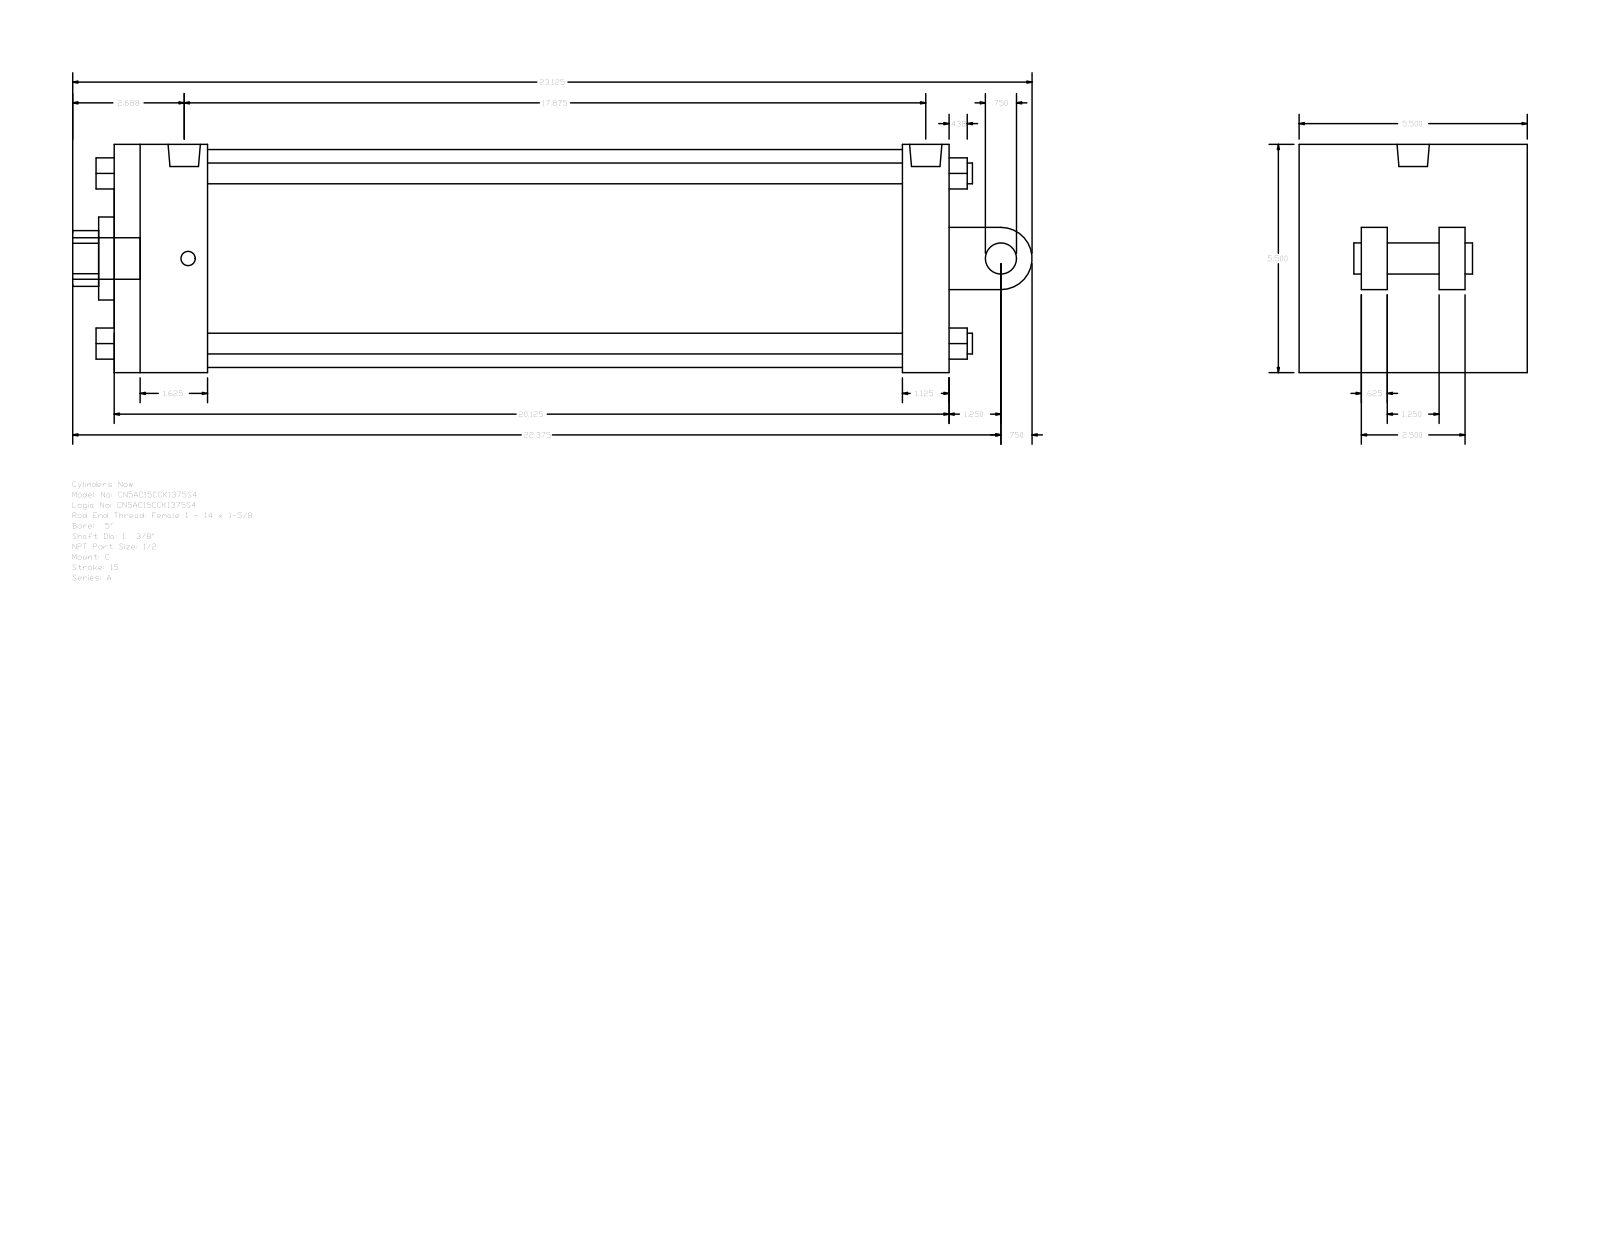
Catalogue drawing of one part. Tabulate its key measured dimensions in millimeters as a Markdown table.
| quantity | value |
| --- | --- |
| part name | A_C__0500_1.375 |
| STEP written by | GSSL Pune (CONFIG_CONTROL_DESIGN) |
| units | millimeters |
| bodies | 0 solids, 135 faces (102 planar, 33 cylindrical, 0 other) |
| overall size | 587.38 × 139.7 × 139.7 |
| round holes (diameter × count) | 8.73 × 2, 19.77 × 1, 34.92 × 1, 50.8 × 1, 133.35 × 1 |
| round bosses / shafts (diameter × count) | 12.7 × 4, 8.73 × 2, 25.4 × 1, 19.77 × 1, 19.05 × 1 |
| partial cylindrical surfaces (radius × count) | 17.06 × 1, 19.05 × 1 |
| main face-to-face distances | 139.7, 511.18, 28.58, 57.15, 482.6, 425.45, 454.03, 38.1, 15.87, 53.97 |
| hole center spacings | 2.39 |
